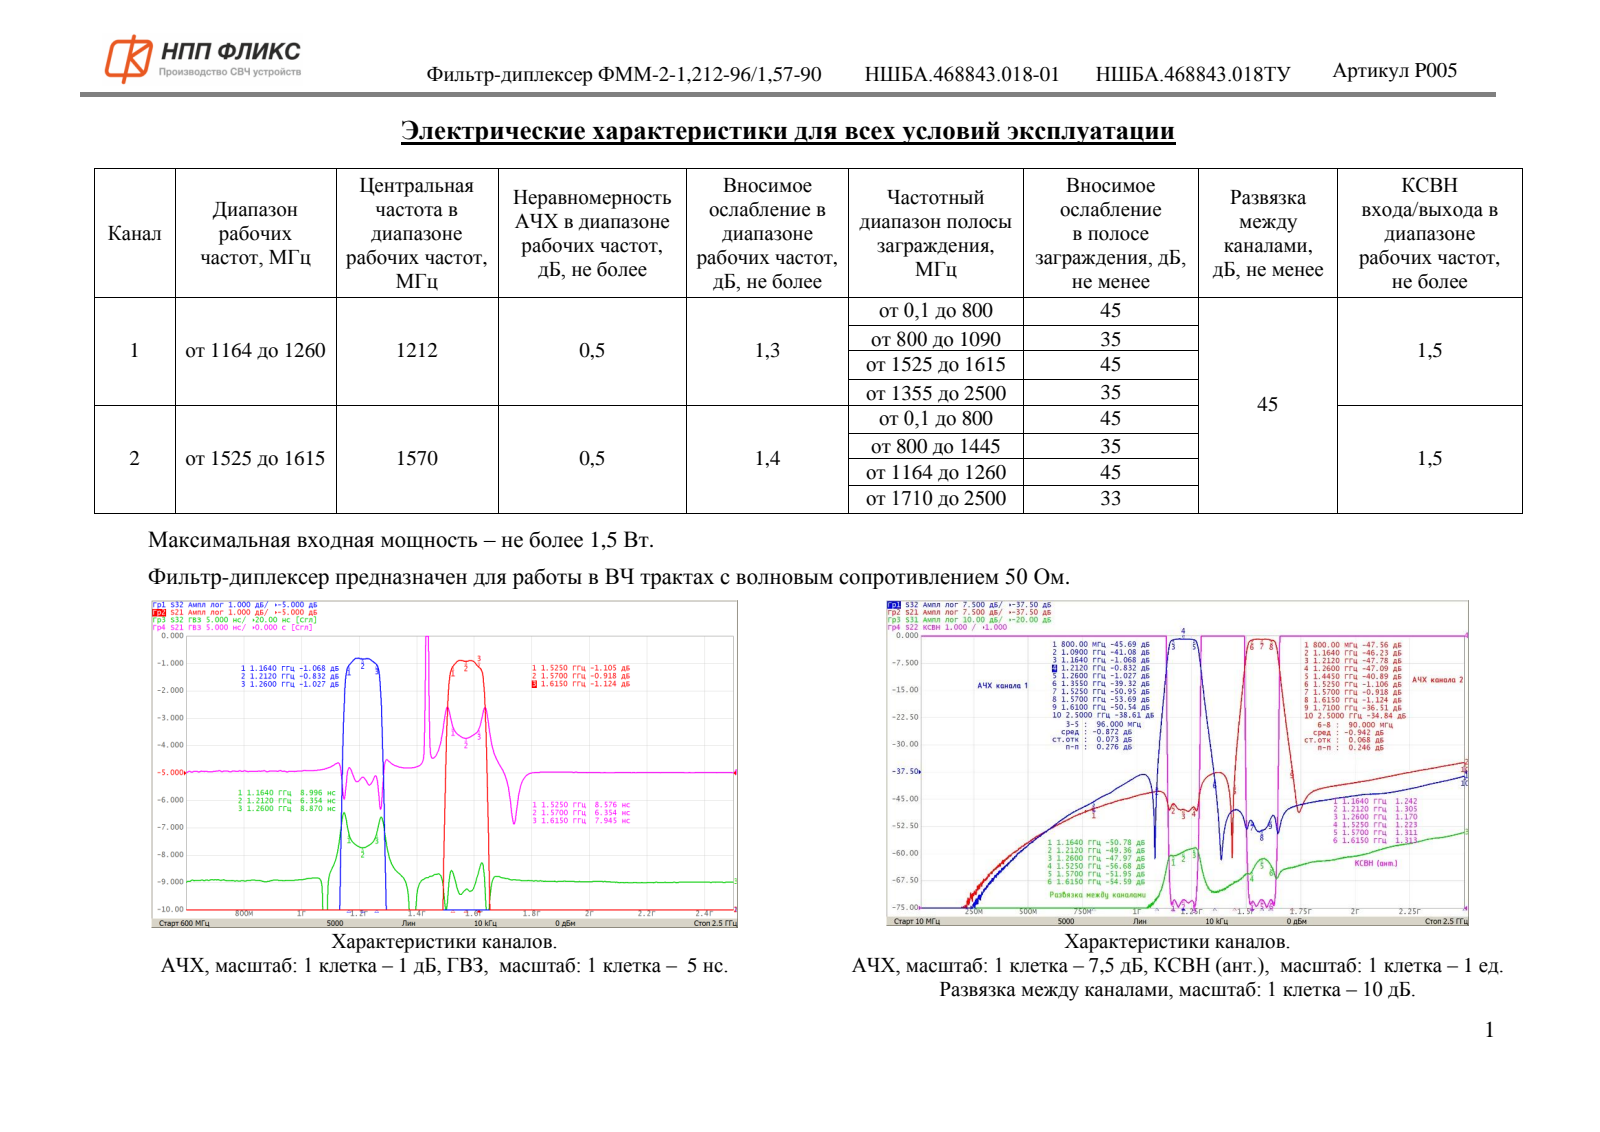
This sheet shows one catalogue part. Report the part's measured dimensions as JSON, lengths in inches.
{"part_name": "НШБА.468843.018-01_Диплексер ФММ-2-1,212-96(1,57-90", "step_written_by": "ASCON Math Kernel (CONFIG_CONTROL_DESIGN)", "units": "inches", "bodies": {"solids": 1, "faces": 974, "planar": 834, "cylindrical": 42, "other": 98}, "overall_size": [0.709, 0.384, 0.165], "volume_in3": 0.034, "surface_area_in2": 1.04, "partial_cylinders_radius": [[0.02, 23], [0.009, 3], [0.008, 2], [0.016, 2], [0.005, 1], [0.014, 1], [0.017, 1]], "face_to_face_distances": [0.165, 0.067, 0.059, 0.309, 0.384, 0.301, 0.376, 0.242, 0.317, 0.075]}
